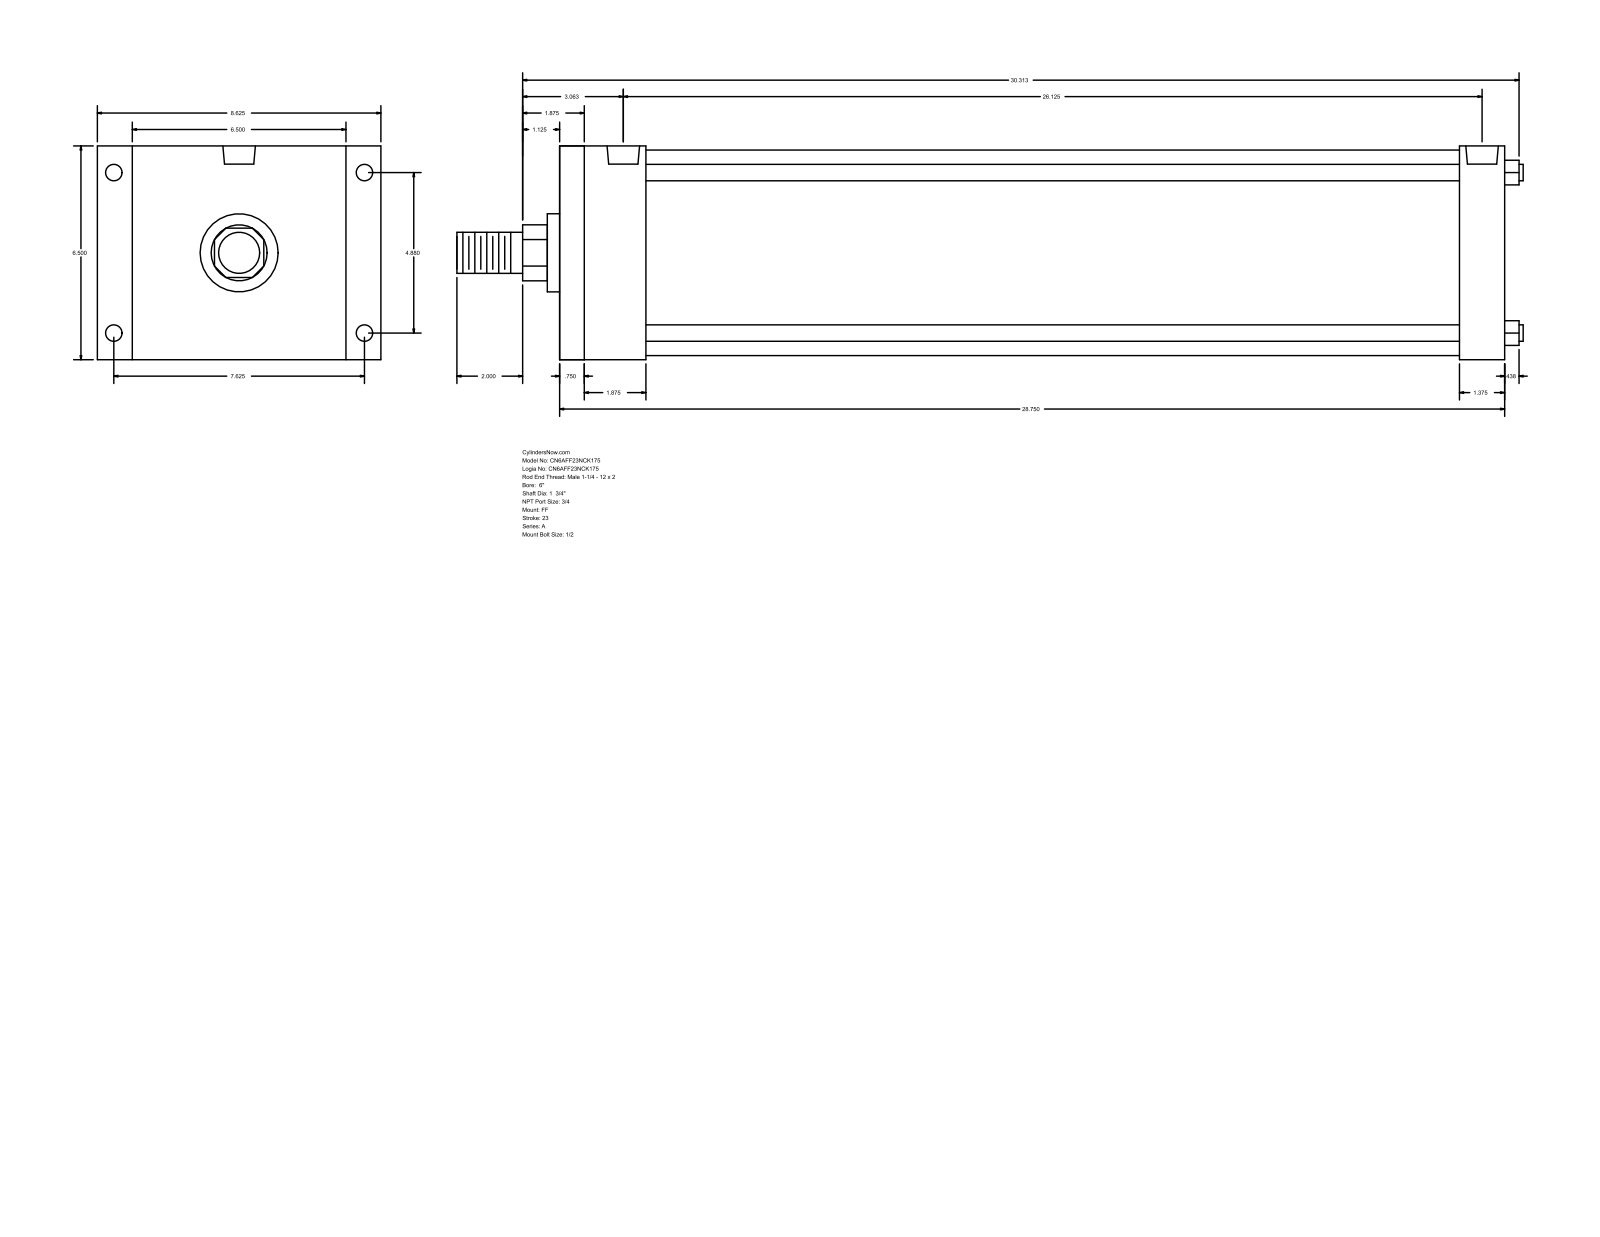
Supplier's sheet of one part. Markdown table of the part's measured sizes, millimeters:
| quantity | value |
| --- | --- |
| part name | A_FF__0600_1.75 |
| STEP written by | GSSL Pune (CONFIG_CONTROL_DESIGN) |
| units | millimeters |
| bodies | 0 solids, 92 faces (64 planar, 28 cylindrical, 0 other) |
| overall size | 823.91 × 219.07 × 165.1 |
| round holes (diameter × count) | 12.7 × 4, 15.08 × 4, 25.12 × 2 |
| round bosses / shafts (diameter × count) | 12.7 × 4, 158.75 × 1, 60.33 × 1, 44.45 × 1, 31.75 × 1 |
| partial cylindrical surfaces (radius × count) | 21.63 × 1 |
| main face-to-face distances | 165.1, 730.26, 19.05, 711.21, 66.68, 47.63, 663.58, 695.33, 676.28, 628.65 |
| hole center spacings | 5.56, 123.96, 193.68, 229.95, 652.45, 658.01, 663.57 |
